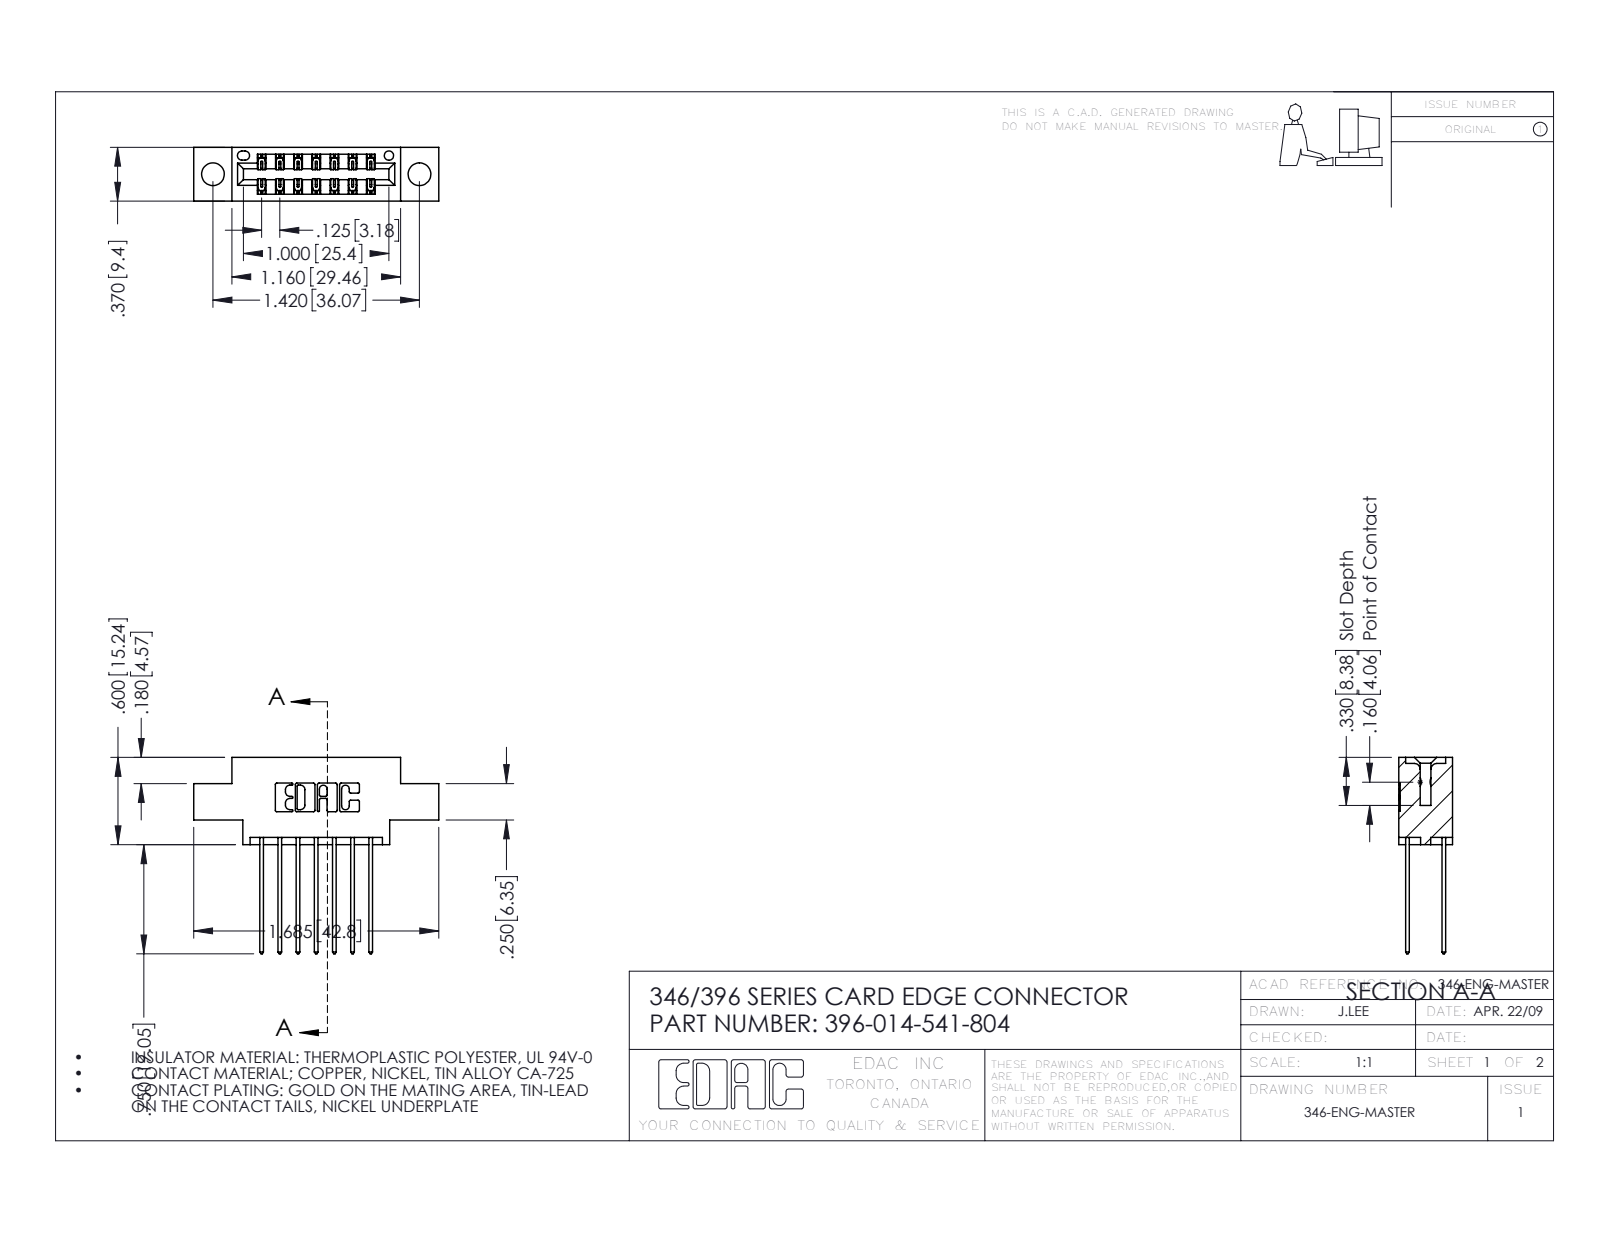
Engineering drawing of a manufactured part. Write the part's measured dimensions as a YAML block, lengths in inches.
part_name: "345-292-001_345-293-141; 346 Part_0.170 Offset - 0.156 Dia-TH; 396-014-541-804"
step_written_by: "SolidWorks 2016 (CONFIG_CONTROL_DESIGN)"
units: inches
bodies: {solids: 15, faces: 854, planar: 570, cylindrical: 284, other: 0}
overall_size: [1.685, 1.35, 0.37]
volume: 0.228
surface_area: 7.701
round_holes:
  - {diameter: 0.156, count: 2}
  - {diameter: 0.064, count: 1}
partial_cylinders:
  - {radius: 0.01, count: 22}
  - {radius: 0.006, count: 21}
  - {radius: 0.01, count: 14}
  - {radius: 0.007, count: 6}
  - {radius: 0.031, count: 6}
  - {radius: 0.026, count: 3}
  - {radius: 0.014, count: 2}
  - {radius: 0.022, count: 2}
face_to_face_distances: [0.25, 0.048, 0.322, 0.37, 0.072, 0.298, 0.025, 0.275, 0.225, 0.148]
hole_center_spacings: [0.246, 1.217, 1.42]
